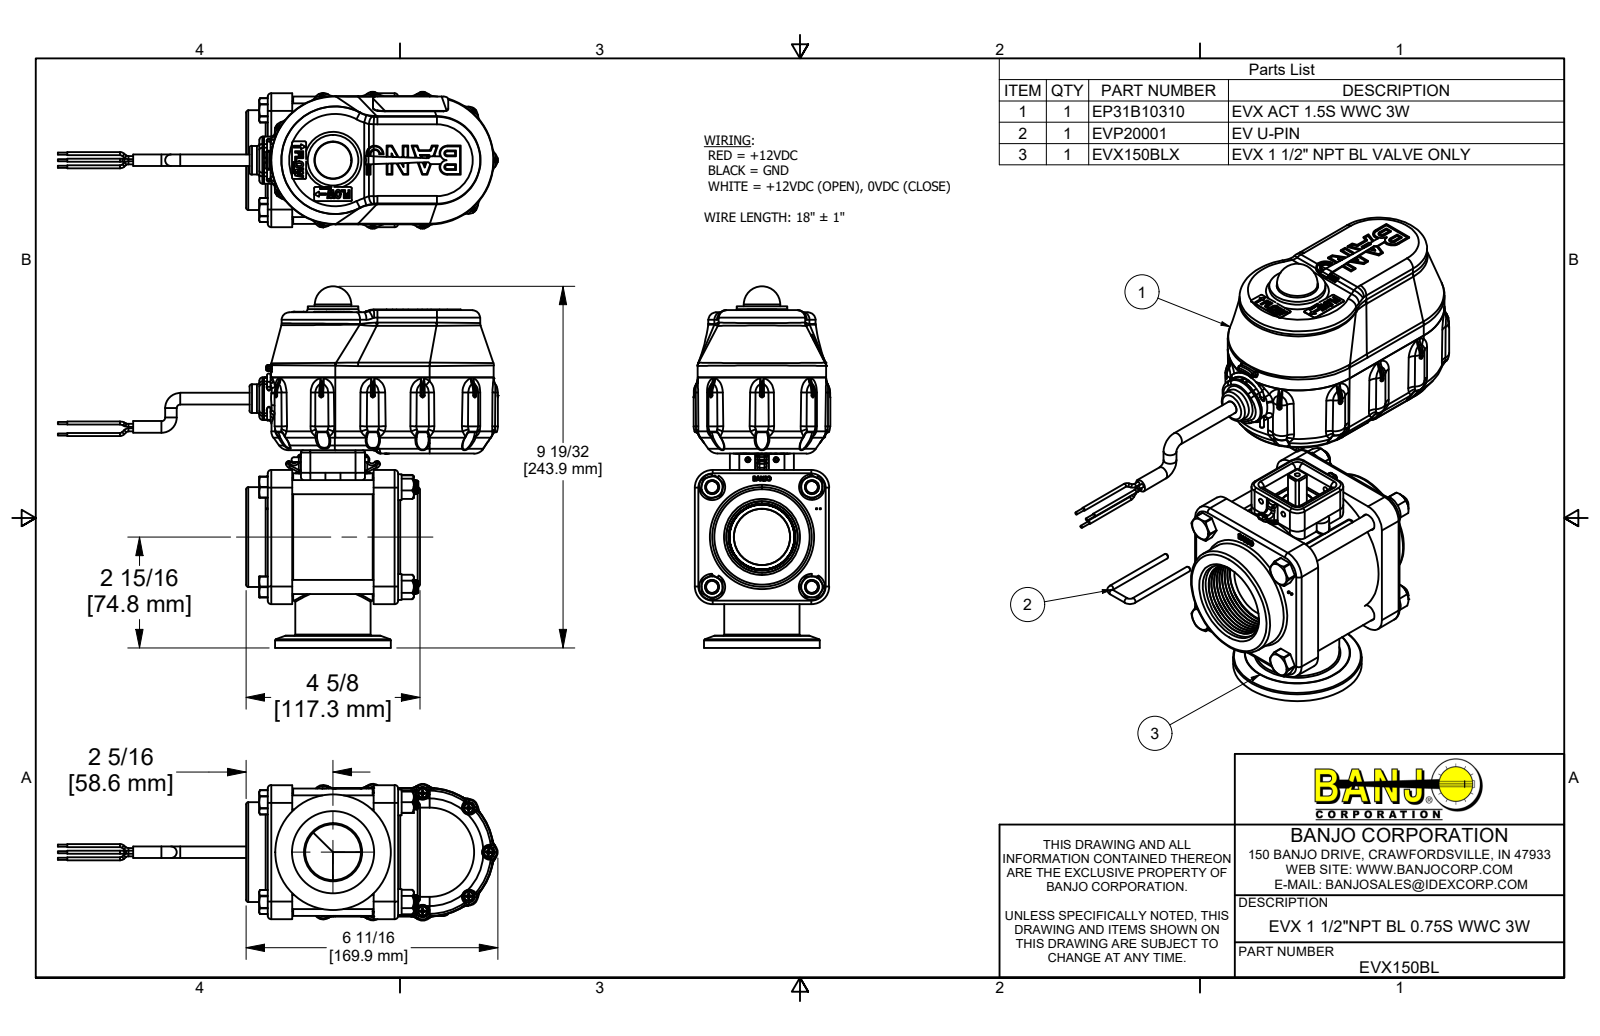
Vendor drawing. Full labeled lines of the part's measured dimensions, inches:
Part name (STEP PRODUCT): EVX150BL; EP31B10310; B61905PPHS; B632038PM (+8 more)
STEP written by: Autodesk Inventor 2019 (AUTOMOTIVE_DESIGN)
Units: inches
Bodies: 98 solids, 11822 faces (3257 planar, 3336 cylindrical, 5229 other)
Overall size (bounding box): 11.685 × 9.602 × 3.63
Volume: 65.43 in³ · Surface area: 672.9 in²
Round holes (diameter × count): ⌀0.095 ×11, ⌀0.15 ×11, ⌀0.08 ×7, ⌀0.107 ×4, ⌀0.126 ×4, ⌀0.136 ×4, ⌀0.148 ×4, ⌀0.15 ×4, ⌀0.17 ×4, ⌀0.307 ×4, ⌀0.385 ×4, ⌀0.406 ×4
Round bosses / shafts (diameter × count): ⌀0.324 ×60, ⌀0.25 ×17, ⌀0.08 ×15, ⌀0.14 ×11, ⌀0.108 ×11, ⌀0.085 ×11, ⌀0.058 ×6, ⌀0.375 ×5
Partial cylindrical surfaces — rounded edges, fillets, slot ends (radius × count): R0.013 ×180, R0.04 ×145, R0.01 ×84, R0.02 ×80, R0.005 ×53, R0.03 ×30, R0.06 ×28, R0.08 ×28
Main face-to-face distances: 0.1, 2.565, 0.65, 2.808, 0.211, 0.06, 0.151, 1.896, 1.836, 1.685
Hole centre spacings: 1.872, 2.648, 2.656, 1.662, 1.774, 2.088, 2.69, 2.73
